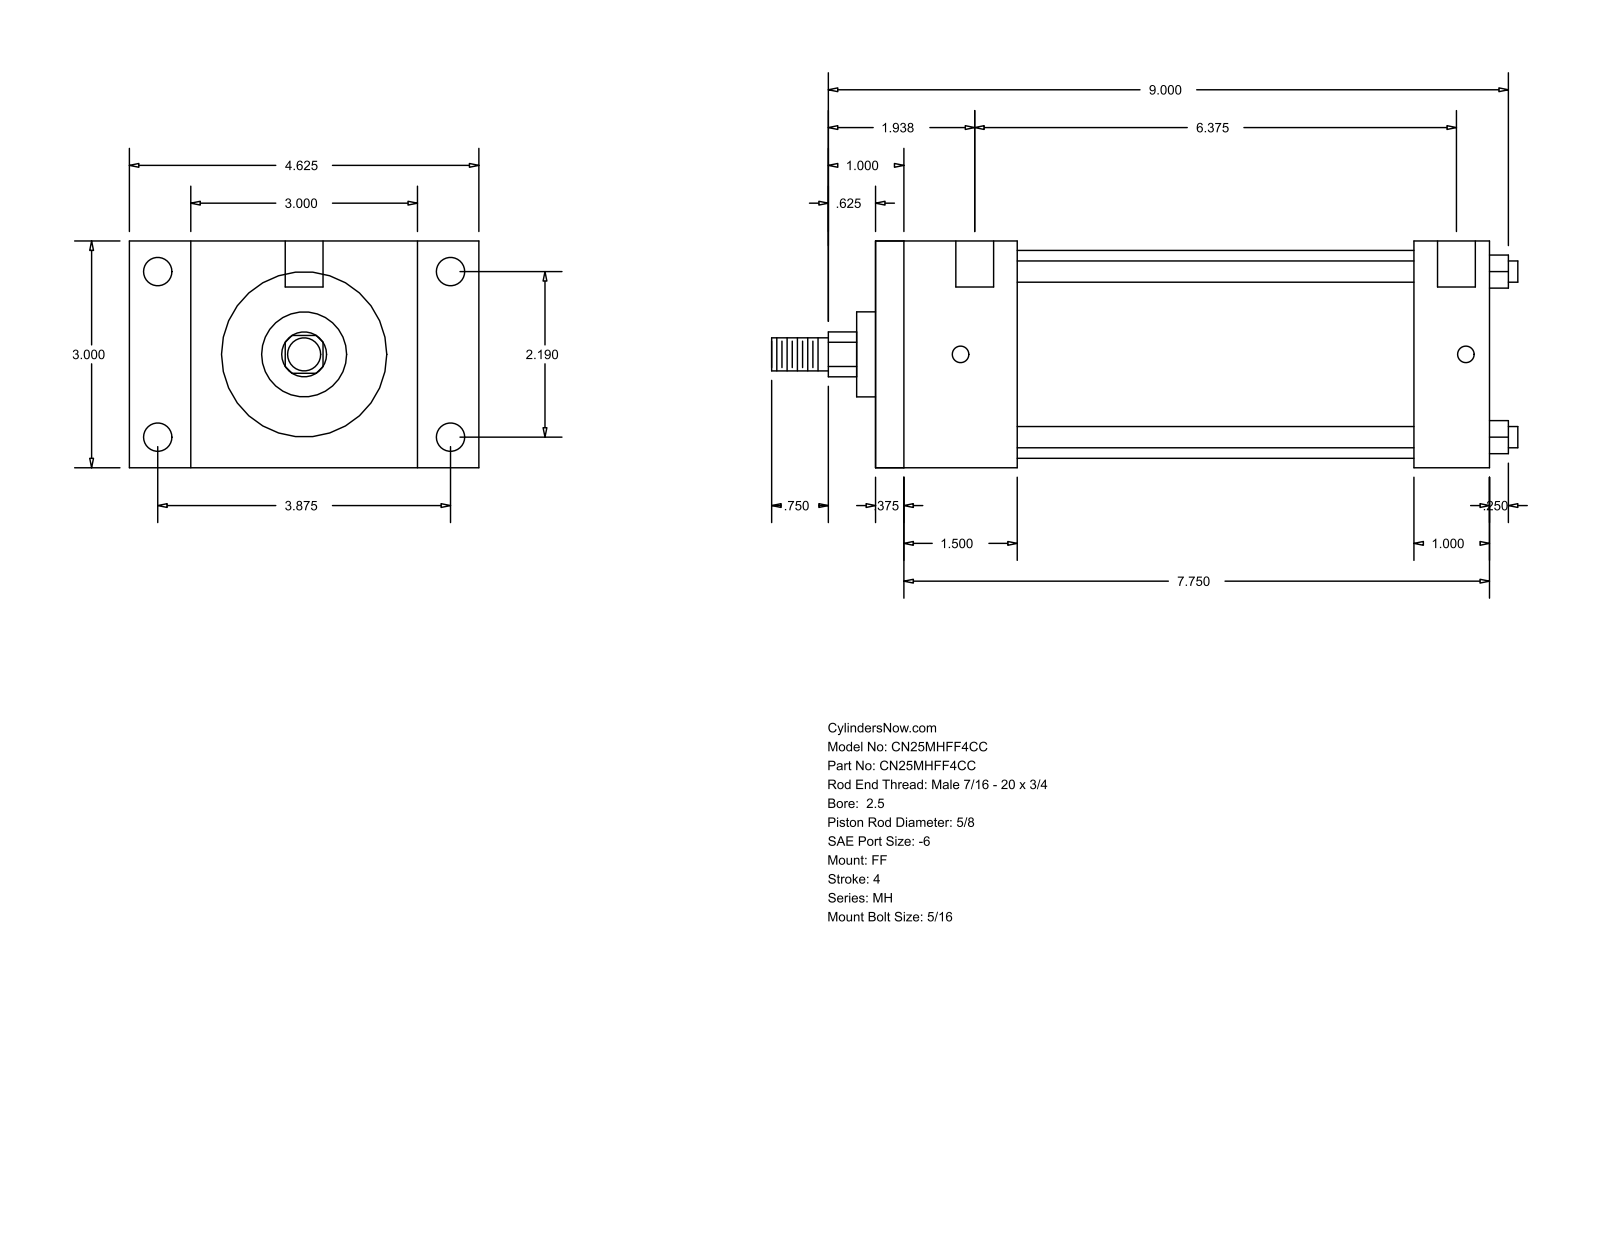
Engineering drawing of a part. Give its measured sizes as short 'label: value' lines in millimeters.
name: MH_FF__0250_0.625
written by: GSSL Pune (CONFIG_CONTROL_DESIGN)
unit: mm
bodies: 0 solids, 92 faces (64 planar, 28 cylindrical, 0 other)
size: 250.82 × 117.47 × 76.2
holes: 4× ⌀5.56, 4× ⌀9.53, 2× ⌀12.7
bosses: 4× ⌀7.14, 1× ⌀69.85, 1× ⌀28.57, 1× ⌀15.88, 1× ⌀11.11
rounds: 1× R7.54
face distances: 76.2, 206.37, 196.85, 9.52, 25.4, 47.62, 180.97, 38.1, 171.45, 133.35
hole spacings: 55.62, 98.42, 113.05, 169.86, 3.17, 4.76, 161.93, 165.1
